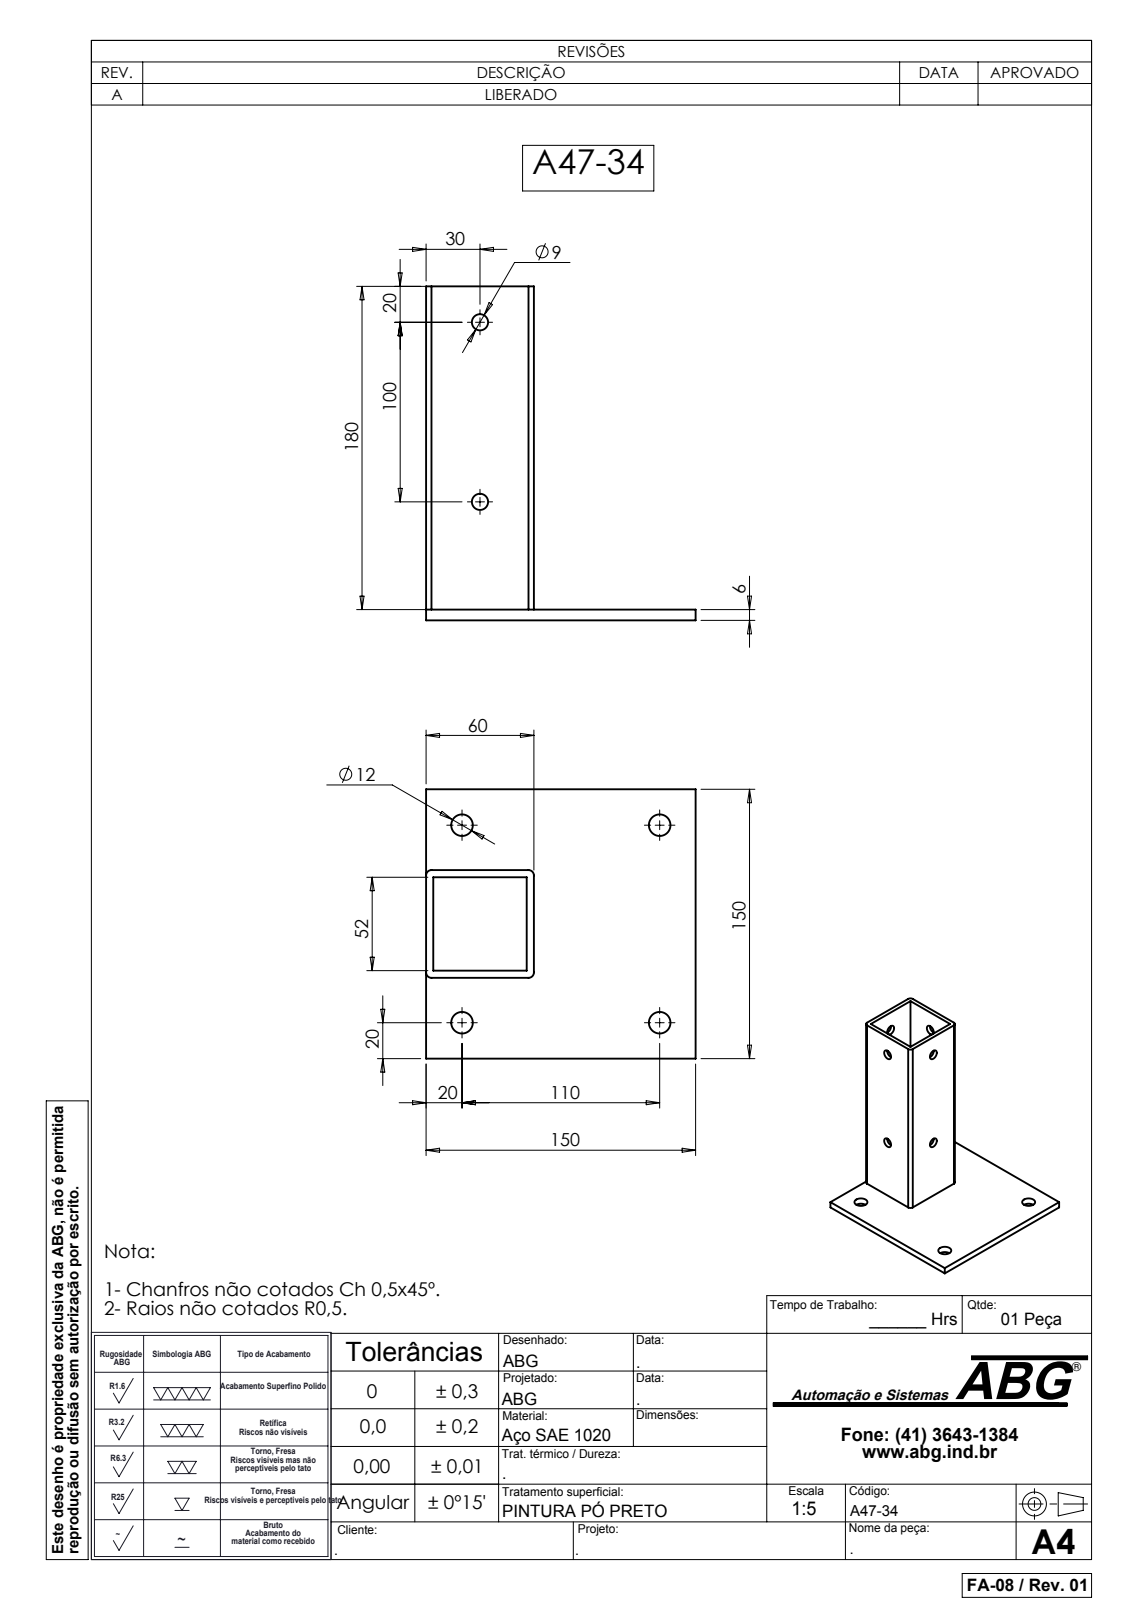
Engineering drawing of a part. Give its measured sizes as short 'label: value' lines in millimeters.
name: A47-34
written by: SolidWorks 2007 (CONFIG_CONTROL_DESIGN)
unit: mm
bodies: 1 solid, 43 faces (15 planar, 28 cylindrical, 0 other)
size: 186 × 150 × 150
volume: 290 139 mm³; area: 128 200 mm²
holes: 4× ⌀9, 4× ⌀12
rounds: 4× R3
face distances: 4, 56, 6, 60, 52, 45, 49, 101, 105, 150
hole spacings: 110, 100, 155.56
